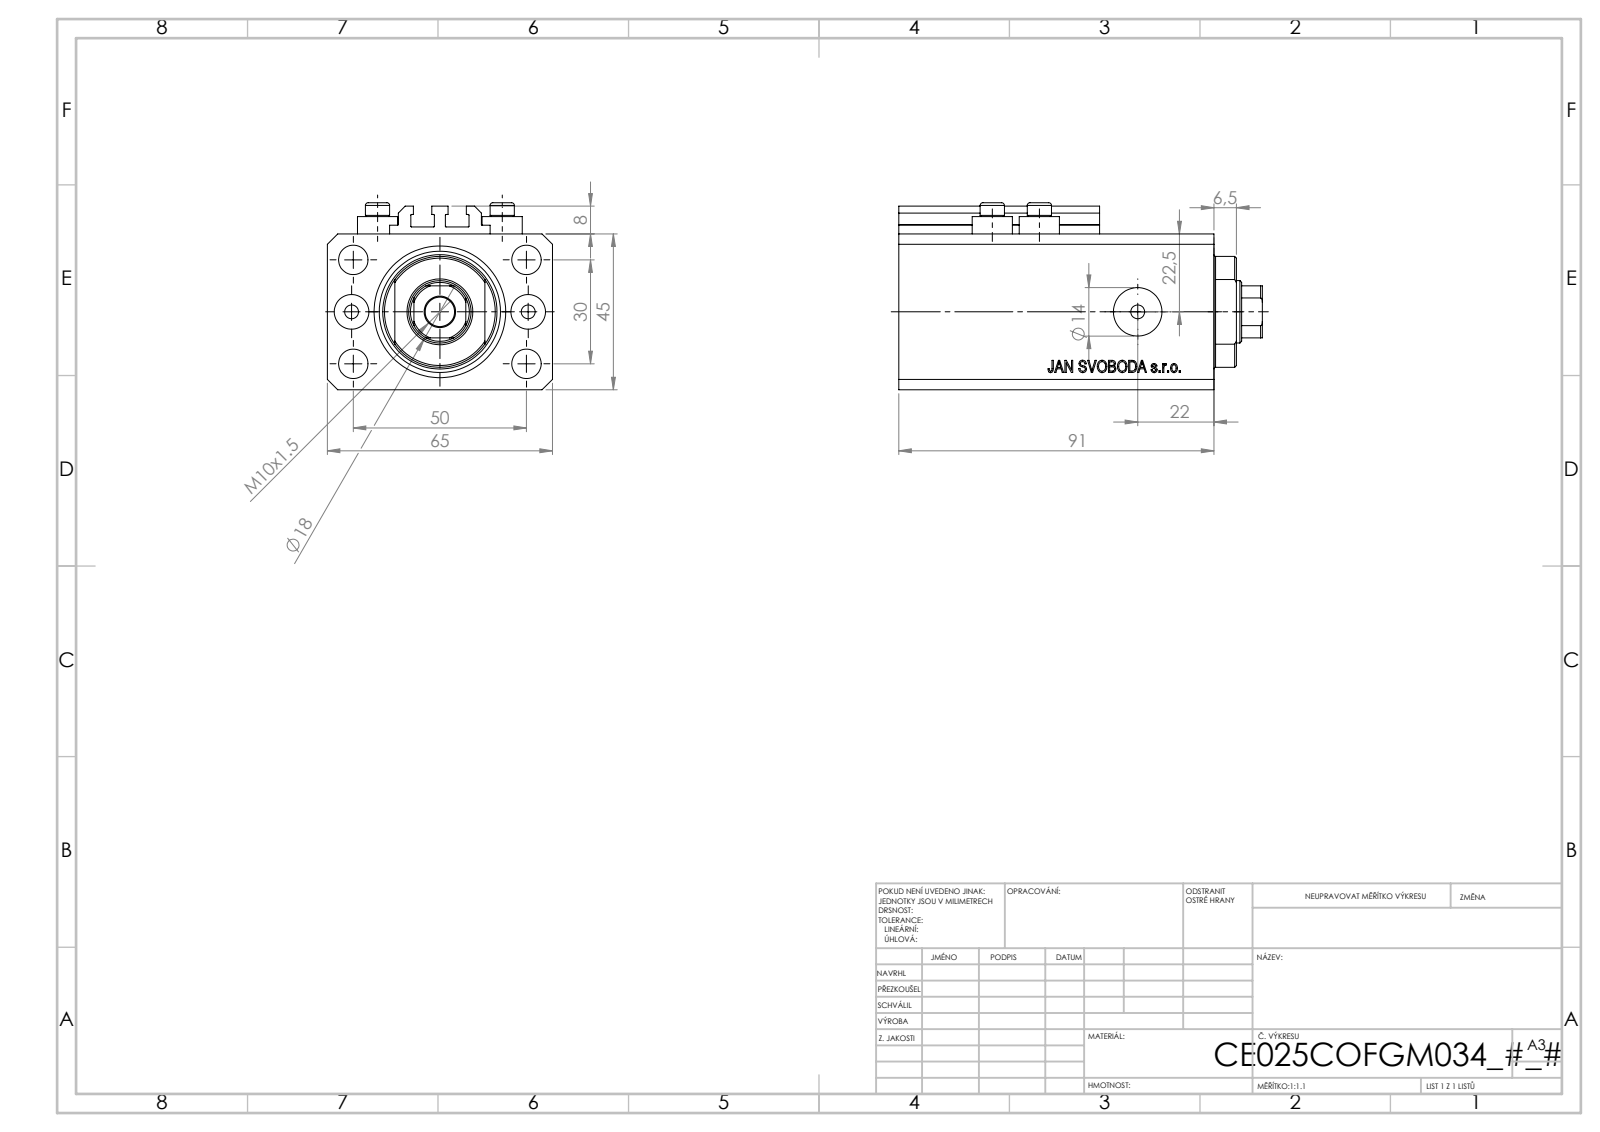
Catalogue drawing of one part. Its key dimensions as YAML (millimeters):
part_name: "V250CE_C_VCP; V250CE_C_Body; V250CE_VC_C; ALLEN BOLT V250CE"
step_written_by: "SolidWorks 2019 (CONFIG_CONTROL_DESIGN)"
units: millimeters
bodies: {solids: 8, faces: 1034, planar: 504, cylindrical: 86, other: 444}
overall_size: [105, 65, 54]
volume: 247916
surface_area: 65045
round_holes:
  - {diameter: 4, count: 8}
  - {diameter: 8.5, count: 5}
  - {diameter: 10, count: 2}
  - {diameter: 14, count: 2}
  - {diameter: 18, count: 1}
  - {diameter: 25, count: 1}
  - {diameter: 38, count: 1}
round_bosses_or_shafts:
  - {diameter: 11.6, count: 4}
  - {diameter: 7, count: 4}
partial_cylinders:
  - {radius: 0.2, count: 10}
  - {radius: 8.5, count: 1}
  - {radius: 16, count: 1}
face_to_face_distances: [45, 65, 14, 77, 91, 47, 6.9, 70.1, 84.1, 3]
hole_center_spacings: [15.01, 29.15, 52.68, 13.6, 25.5, 30, 36, 38.48]
